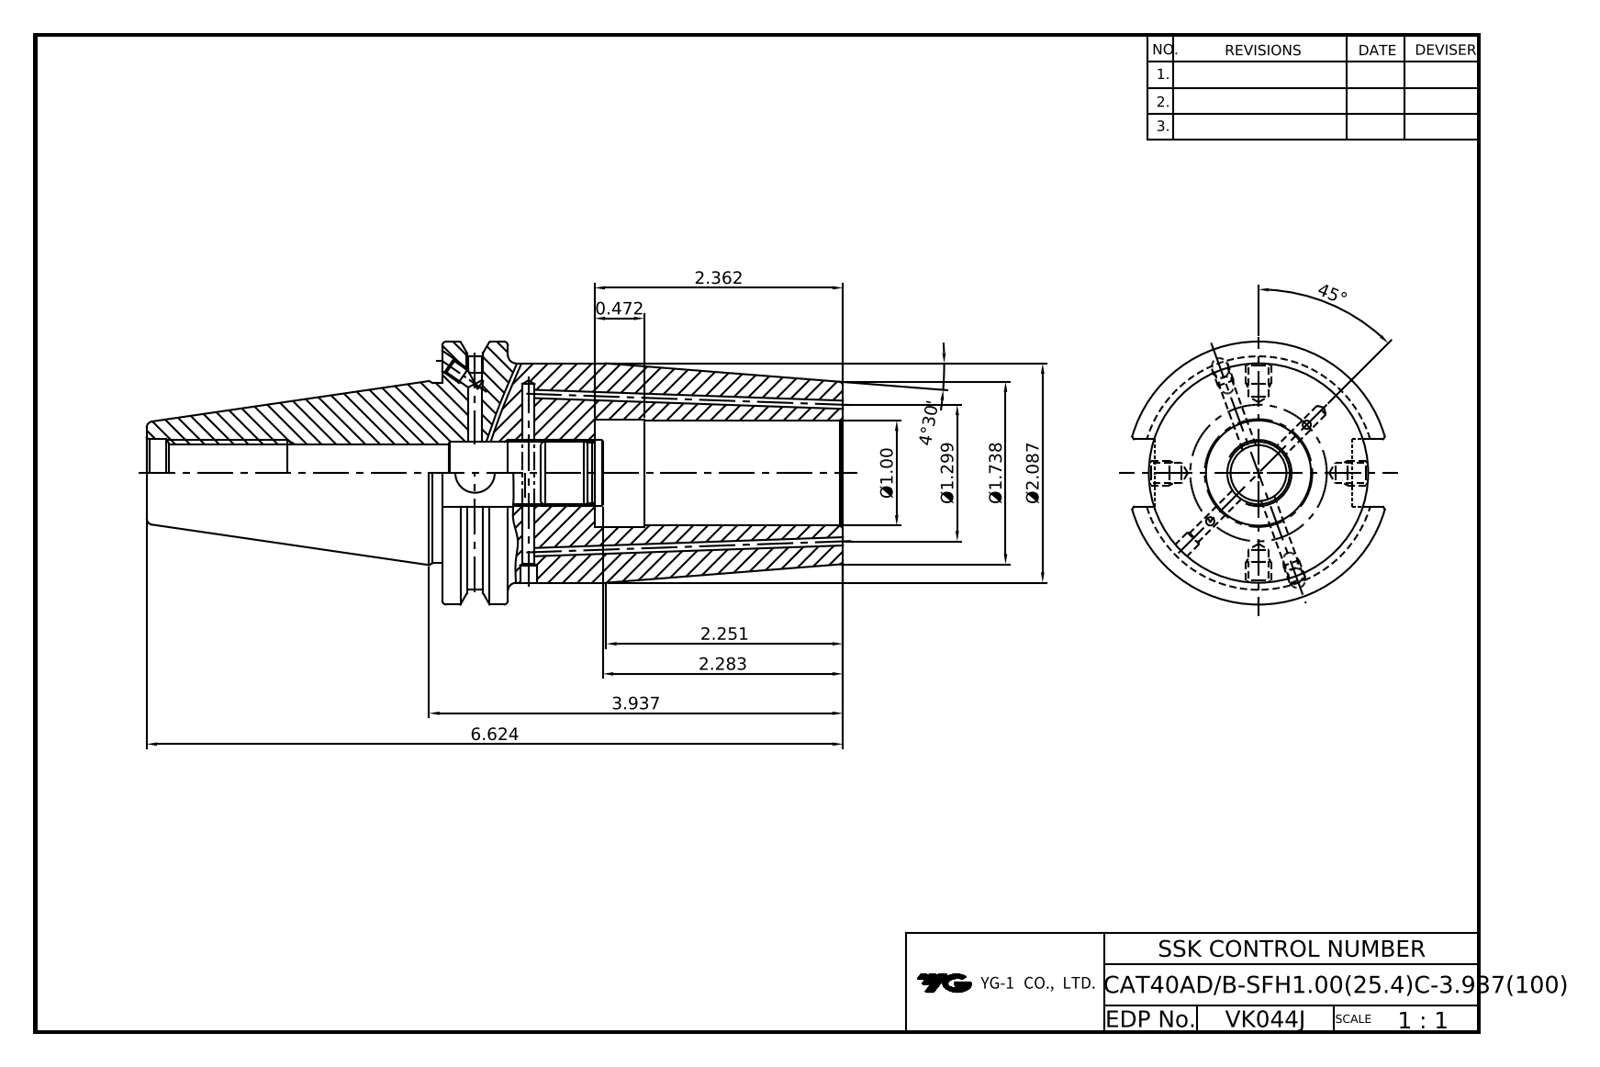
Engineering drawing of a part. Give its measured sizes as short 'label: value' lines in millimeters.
name: LO-CAT40ADB-SFH25.4C-100
written by: Autodesk Inventor 2024 (AUTOMOTIVE_DESIGN)
unit: mm
bodies: 1 solid, 96 faces (42 planar, 31 cylindrical, 23 other)
size: 168.25 × 63.5 × 61.09
volume: 223 430 mm³; area: 39 462 mm²
holes: 4× ⌀3.24, 2× ⌀2.5, 2× ⌀4, 2× ⌀4.2, 1× ⌀9.53, 1× ⌀13, 1× ⌀13.39, 1× ⌀14.92, 1× ⌀16.3, 1× ⌀25.4, 1× ⌀26.6
bosses: 1× ⌀63.5, 1× ⌀53, 1× ⌀43.6
rounds: 1× R28.15
face distances: 96.83, 15.88, 80.95, 36.83, 20.95, 60, 47.6, 16.38, 71.42, 87.3
